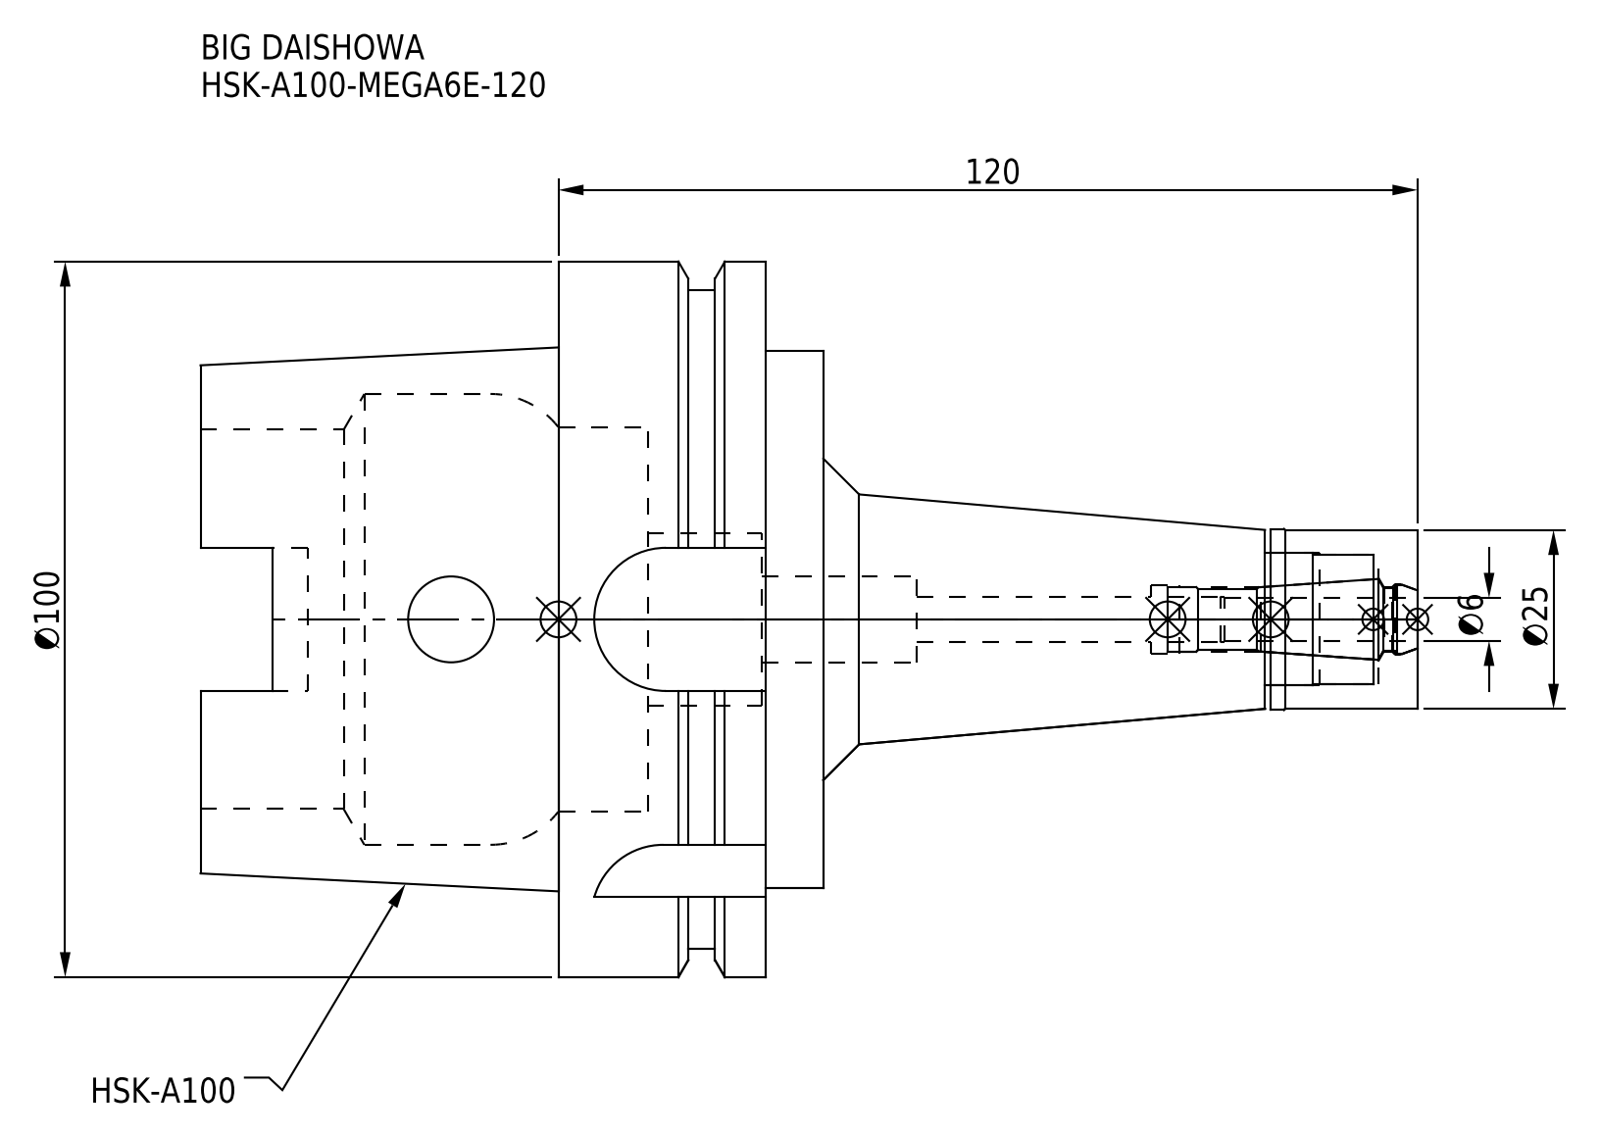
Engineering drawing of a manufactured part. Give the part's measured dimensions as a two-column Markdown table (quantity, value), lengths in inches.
| quantity | value |
| --- | --- |
| part name | MEN6_1.stp; HA100ME06120-060_ASM.stp; HSK-A100-MEGA6E-120; DXF_TEMP_ASSY_ASM_4_ASM.stp (+3 more) |
| STEP written by | SolidWorks 2019 (CONFIG_CONTROL_DESIGN) |
| units | inches |
| bodies | 2 solids, 126 faces (42 planar, 56 cylindrical, 28 other) |
| overall size | 6.693 × 3.937 × 3.937 |
| volume | 20.72 in³ |
| surface area | 98.79 in² |
| round holes (diameter × count) | 0.472 × 2, 0.252 × 1, 0.354 × 1, 0.378 × 1, 0.39 × 1, 0.709 × 1, 0.728 × 1, 0.945 × 1, 2.087 × 1, 2.118 × 1, 2.48 × 1 |
| round bosses / shafts (diameter × count) | 3.937 × 1, 3.622 × 1, 2.953 × 1, 0.996 × 1, 0.984 × 1 |
| partial cylindrical surfaces (radius × count) | 0.192 × 4, 0.394 × 4 |
| main face-to-face distances | 1.142, 0.315, 1.457, 0.967, 0.652, 0.49, 1.969, 3.425, 3.11, 2.459 |
